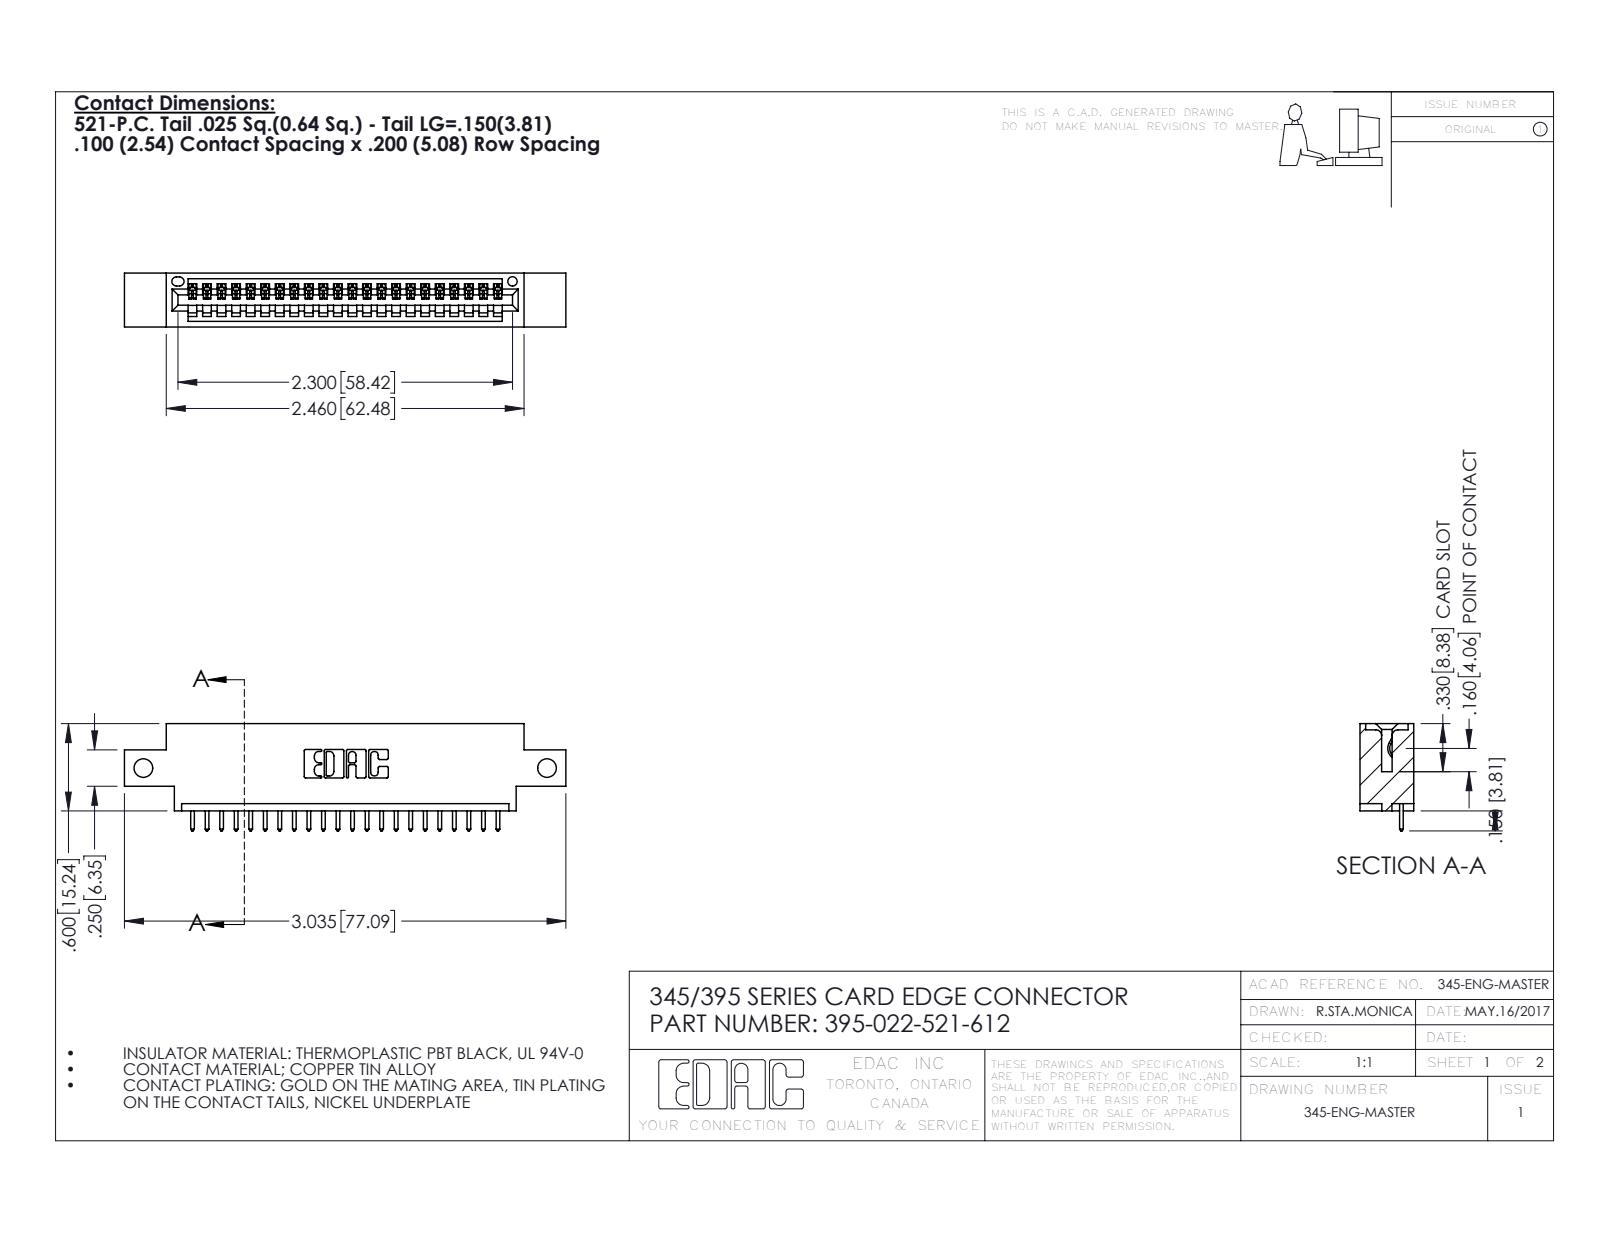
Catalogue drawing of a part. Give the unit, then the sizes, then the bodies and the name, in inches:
Units: inches
Overall size (bounding box): 3.035 × 0.737 × 0.37
Round holes (diameter × count): ⌀0.128 ×2, ⌀0.064 ×1
Partial cylindrical surfaces — rounded edges, fillets, slot ends (radius × count): R0.006 ×44, R0.01 ×44, R0.01 ×22, R0.007 ×6, R0.031 ×6, R0.026 ×3, R0.031 ×2, R0.04 ×2
Main face-to-face distances: 0.298, 0.072, 0.37, 0.2, 0.098, 0.272, 0.025, 0.225, 0.175, 0.15
Hole centre spacings: 2.775
Volume: 0.421 in³ · Surface area: 13.38 in²
Bodies: 23 solids, 1406 faces (964 planar, 442 cylindrical, 0 other)
Part name (STEP PRODUCT): 345-292-001_345-293-121; 395-022-521-612; 345 Part_0.170 Offset - Side Mount
STEP written by: SolidWorks 2016 (CONFIG_CONTROL_DESIGN)
